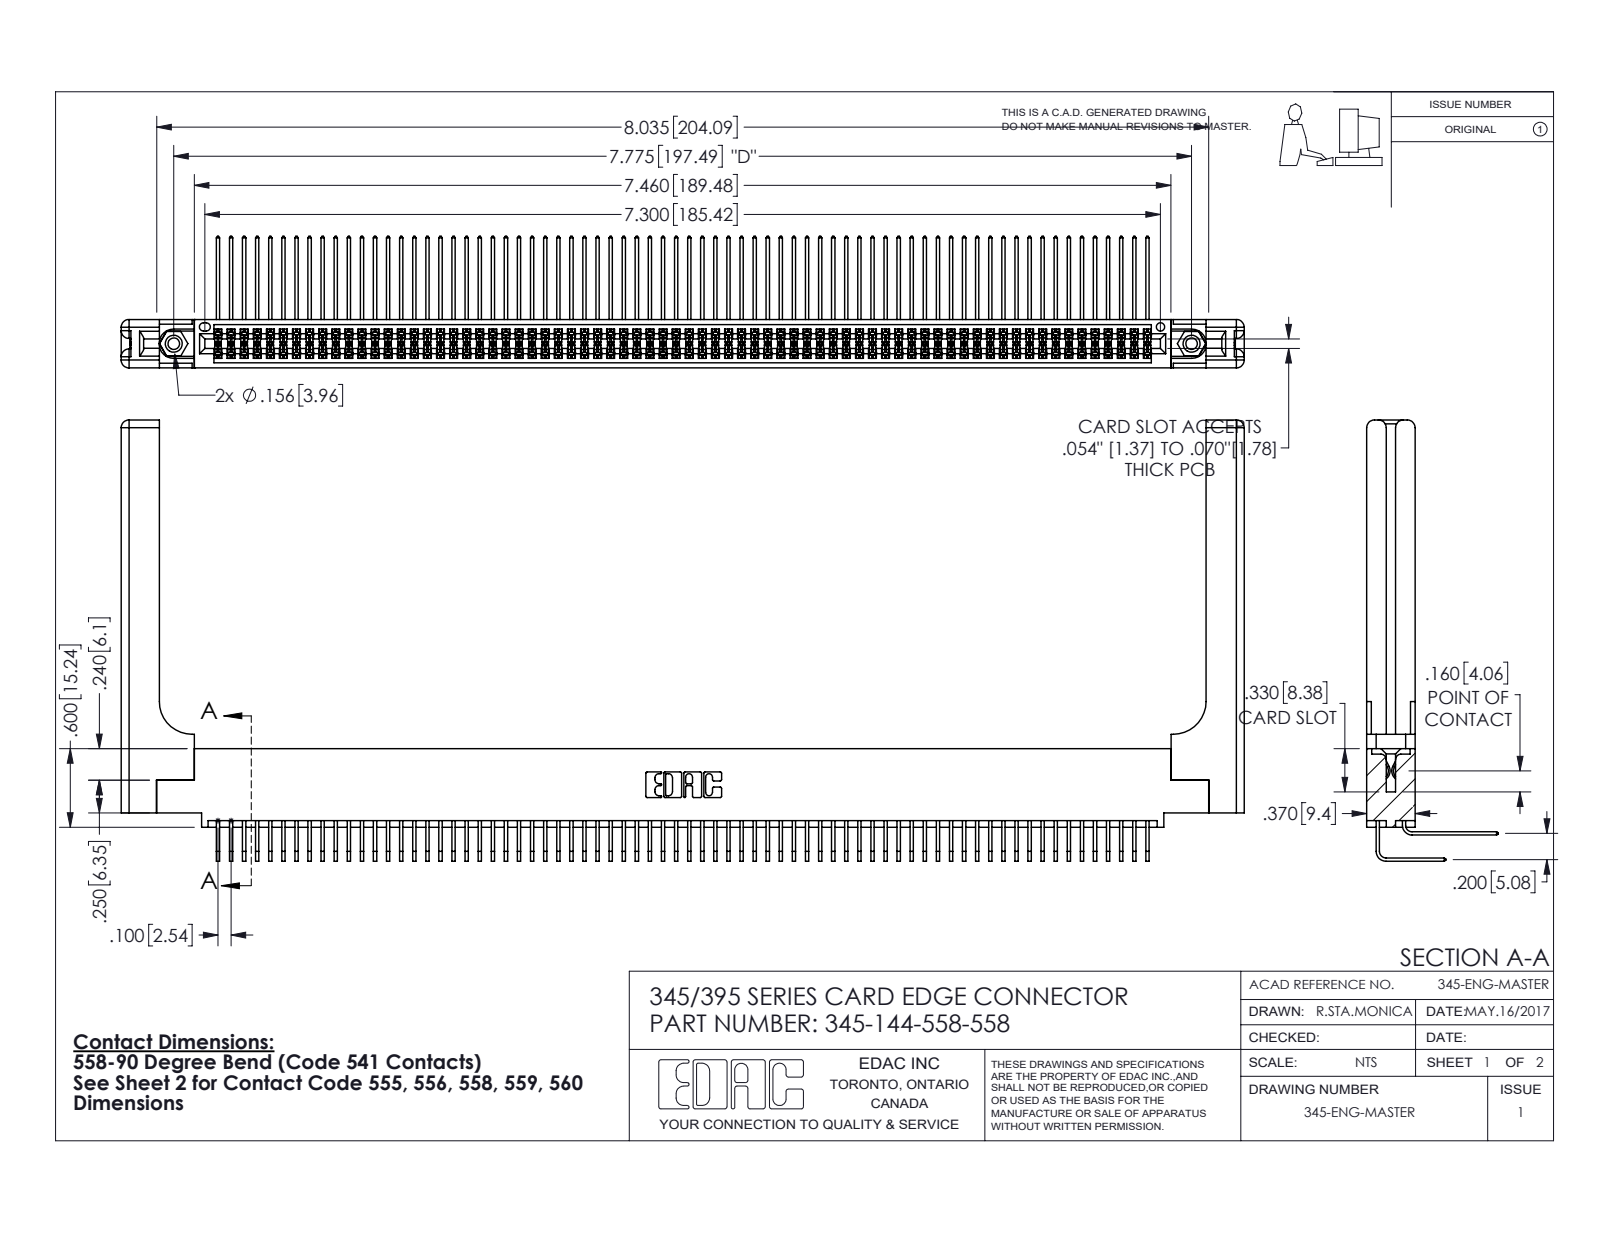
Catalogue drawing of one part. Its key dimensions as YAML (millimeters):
part_name: "345-220-058_345-220-058; 345-292-001_558 Tail - 2; 345-144-558-558; 345 Part_0.110 Offset - 0.156 Dia-TH (+2 more)"
step_written_by: "SolidWorks 2016 (CONFIG_CONTROL_DESIGN)"
units: millimeters
bodies: {solids: 149, faces: 7874, planar: 5272, cylindrical: 2542, other: 60}
overall_size: [217.9, 85.6, 25.5]
volume: 30680
surface_area: 42460
round_holes:
  - {diameter: 2.3, count: 2}
  - {diameter: 3.2, count: 2}
  - {diameter: 4, count: 2}
  - {diameter: 1.6, count: 1}
round_bosses_or_shafts:
  - {diameter: 3.9, count: 2}
partial_cylinders:
  - {radius: 0.2, count: 288}
  - {radius: 0.3, count: 22}
  - {radius: 1.5, count: 16}
  - {radius: 0.2, count: 6}
  - {radius: 0.8, count: 6}
  - {radius: 0.7, count: 3}
  - {radius: 0.4, count: 2}
  - {radius: 0.5, count: 2}
face_to_face_distances: [1.8, 7.6, 9.4, 5.1, 2.5, 6.9, 0.6, 5.7, 0.6, 4.4]
hole_center_spacings: [6.9, 191.5, 197.5]
